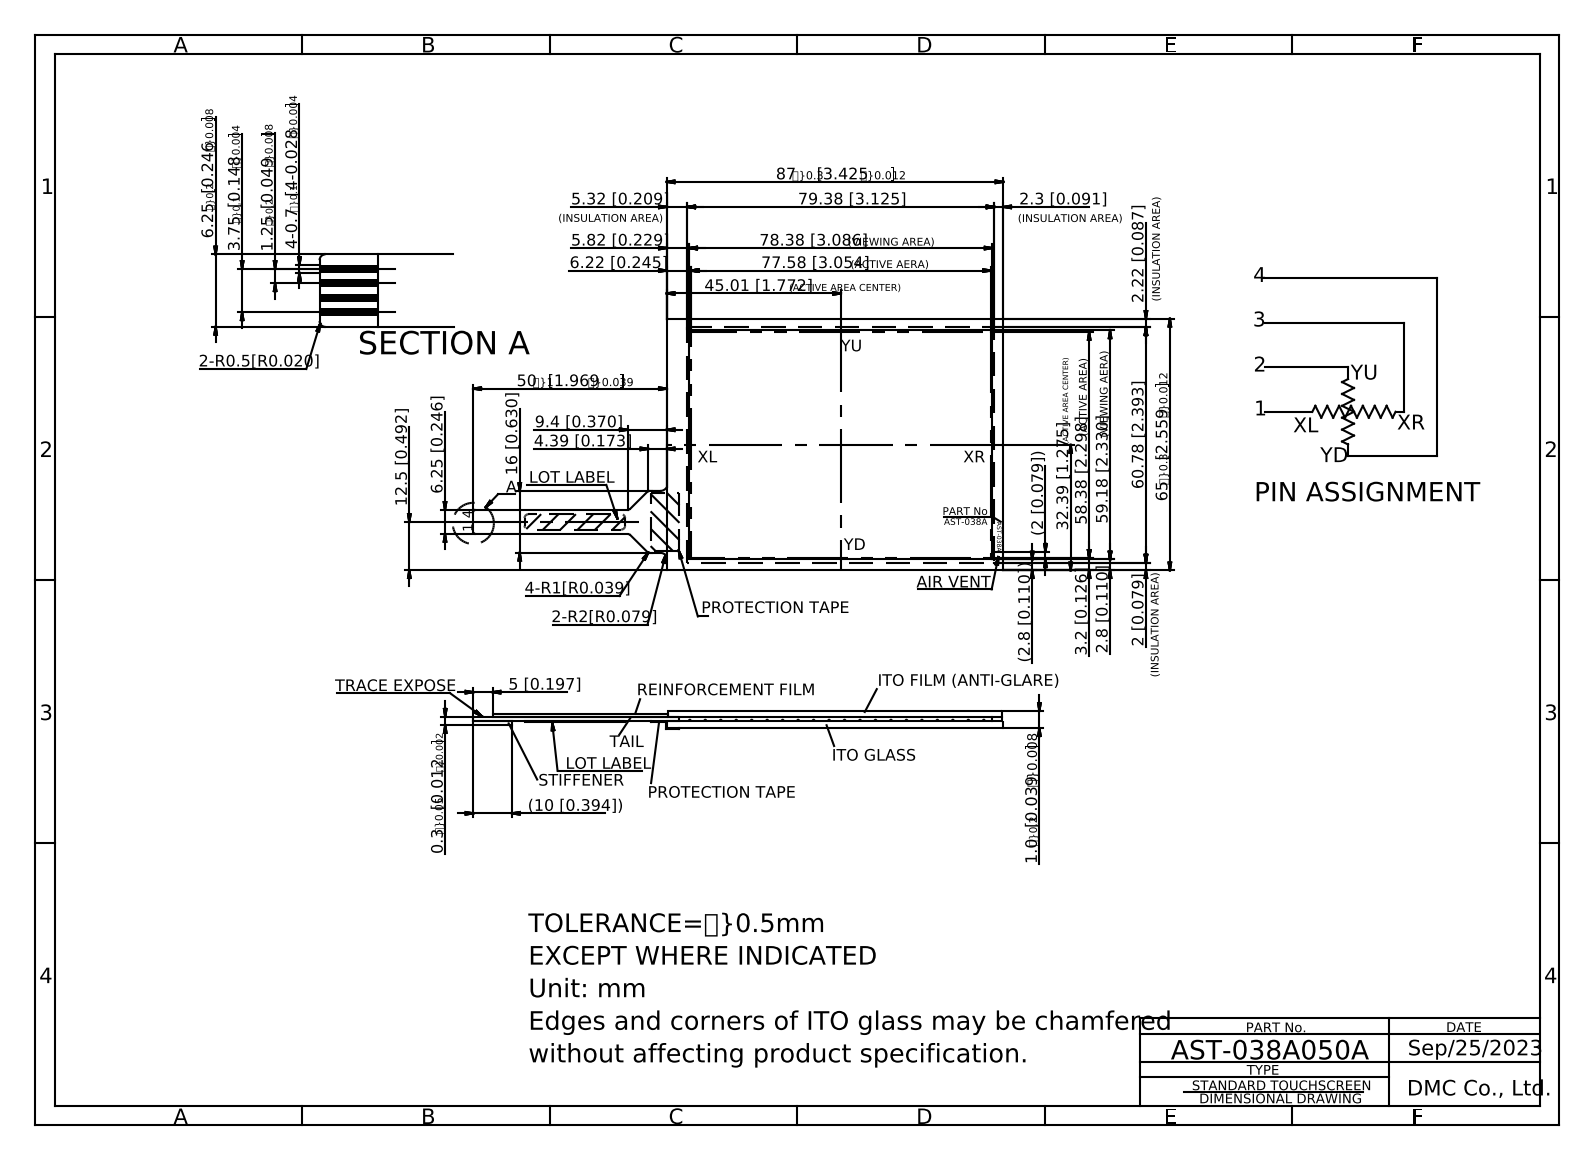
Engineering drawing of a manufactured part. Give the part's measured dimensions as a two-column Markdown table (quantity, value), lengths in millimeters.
| quantity | value |
| --- | --- |
| part name | AST-038A050A |
| STEP written by | Autodesk Inventor 2020 (CONFIG_CONTROL_DESIGN) |
| units | millimeters |
| bodies | 1 solid, 51 faces (45 planar, 6 cylindrical, 0 other) |
| overall size | 137 × 65 × 1 |
| volume | 5 697 mm³ |
| surface area | 12 445 mm² |
| partial cylindrical surfaces (radius × count) | 1 × 4, 0.5 × 2 |
| main face-to-face distances | 1, 0.8, 0.7, 0.4, 0.9, 65, 87, 0.5, 0.6, 0.69 |
